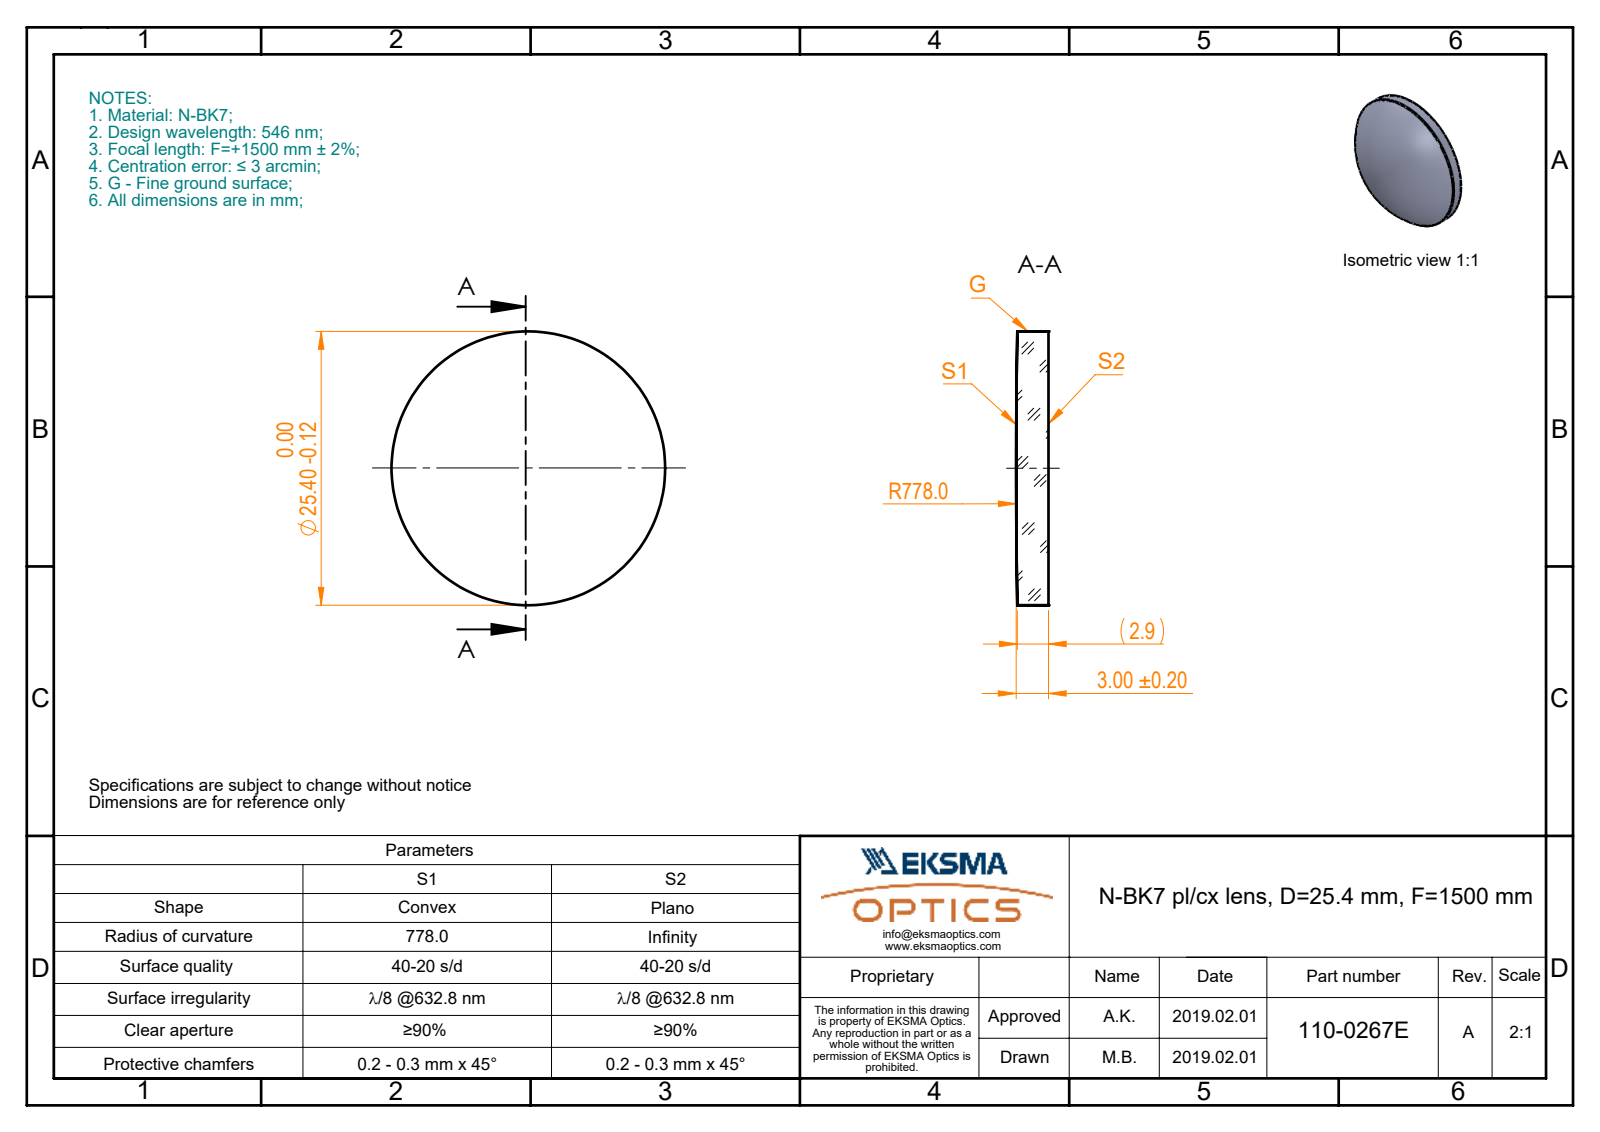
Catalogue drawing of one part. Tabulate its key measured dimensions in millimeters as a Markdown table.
| quantity | value |
| --- | --- |
| part name | 110-0267E BK7 pl-cx 25.4 F1500 |
| STEP written by | SolidWorks 2017 (CONFIG_CONTROL_DESIGN) |
| units | millimeters |
| bodies | 1 solid, 5 faces (1 planar, 2 cylindrical, 2 other) |
| overall size | 25.4 × 25.4 × 3 |
| volume | 1 494 mm³ |
| surface area | 1 245 mm² |
| round bosses / shafts (diameter × count) | 25.4 × 1 |
